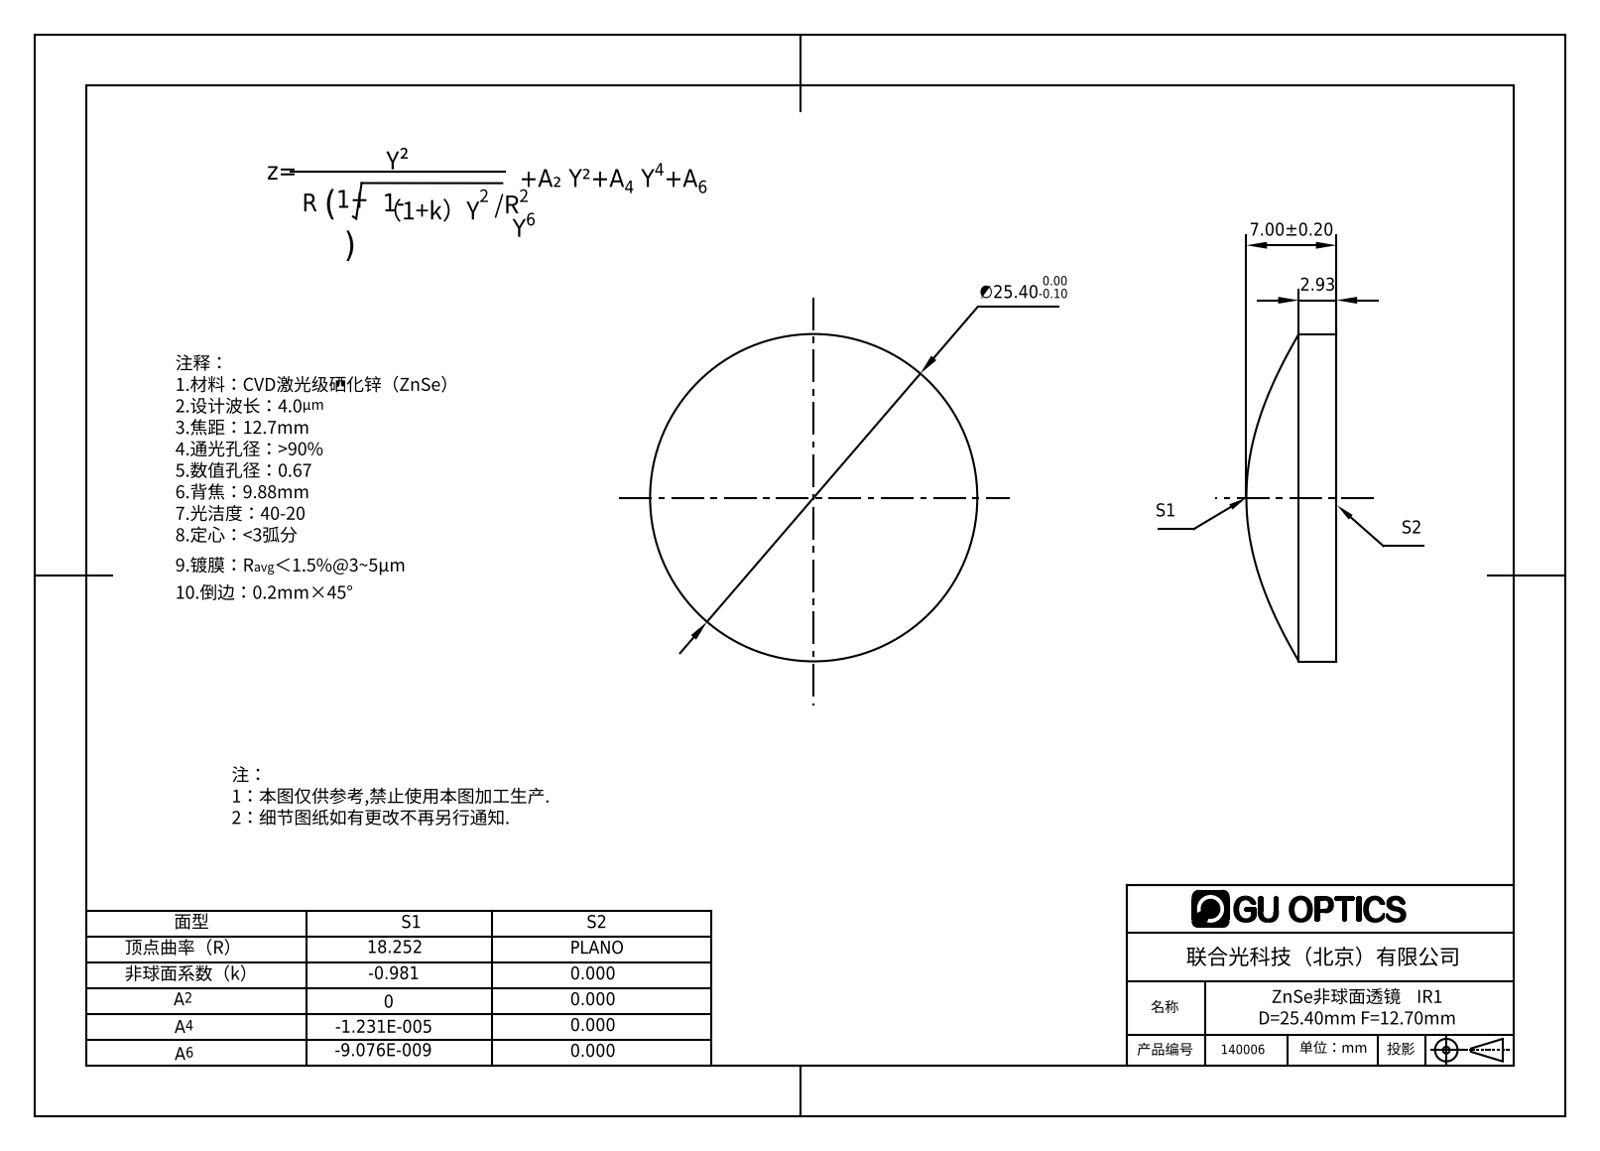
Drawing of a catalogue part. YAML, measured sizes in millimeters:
part_name: "140006"
step_written_by: "SolidWorks 2020 (CONFIG_CONTROL_DESIGN)"
units: millimeters
bodies: {solids: 1, faces: 5, planar: 1, cylindrical: 2, other: 2}
overall_size: [25.4, 25.4, 7]
volume: 2485
surface_area: 1294
round_bosses_or_shafts:
  - {diameter: 25.4, count: 1}
